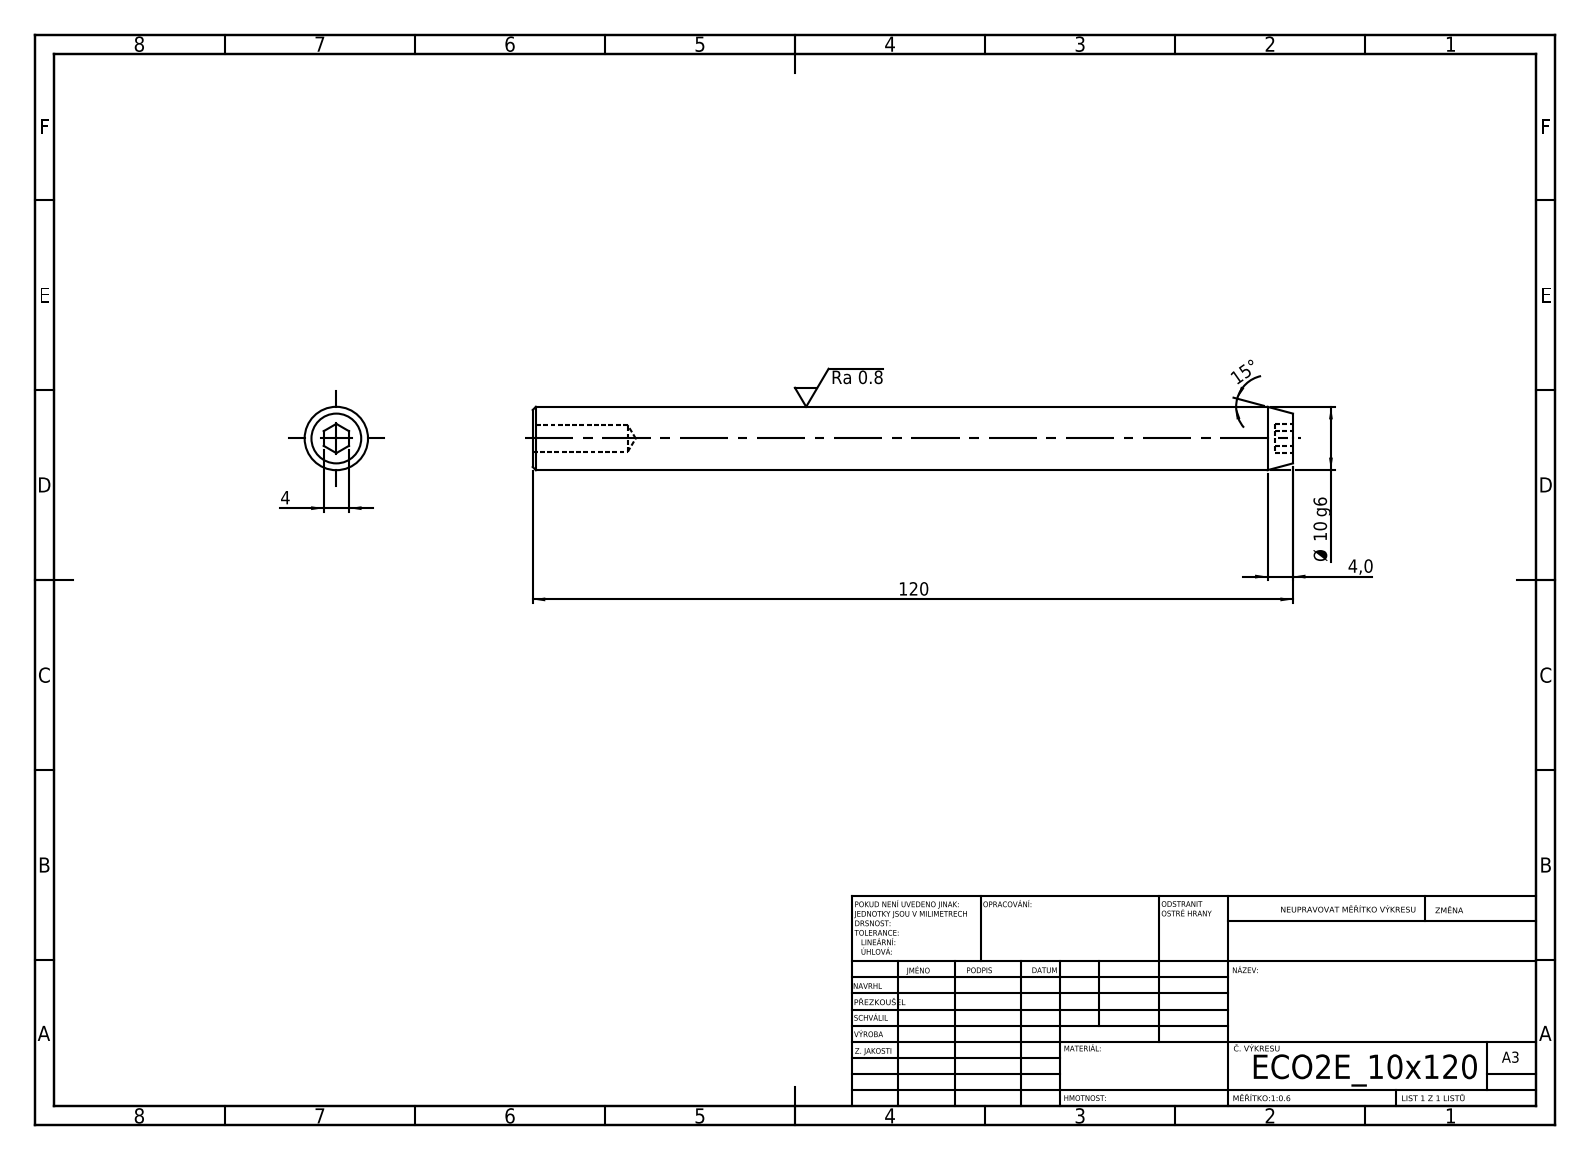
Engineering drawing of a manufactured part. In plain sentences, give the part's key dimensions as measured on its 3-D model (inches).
Its 3-D file was written by "SolidWorks 2019 (CONFIG_CONTROL_DESIGN)". It is 1 solid with 19 faces: 9 planar, 4 cylindrical and 6 other. Overall it measures 4.724 by 0.394 by 0.394 inches. Its volume is 0.556 cubic inches and its surface area 6.381 square inches. Round holes: 1 of diameter 0.165. Round bosses or shafts: 1 of diameter 0.394. The main face-to-face distances are 4.724, 0.157, 0.11, 4.614.
